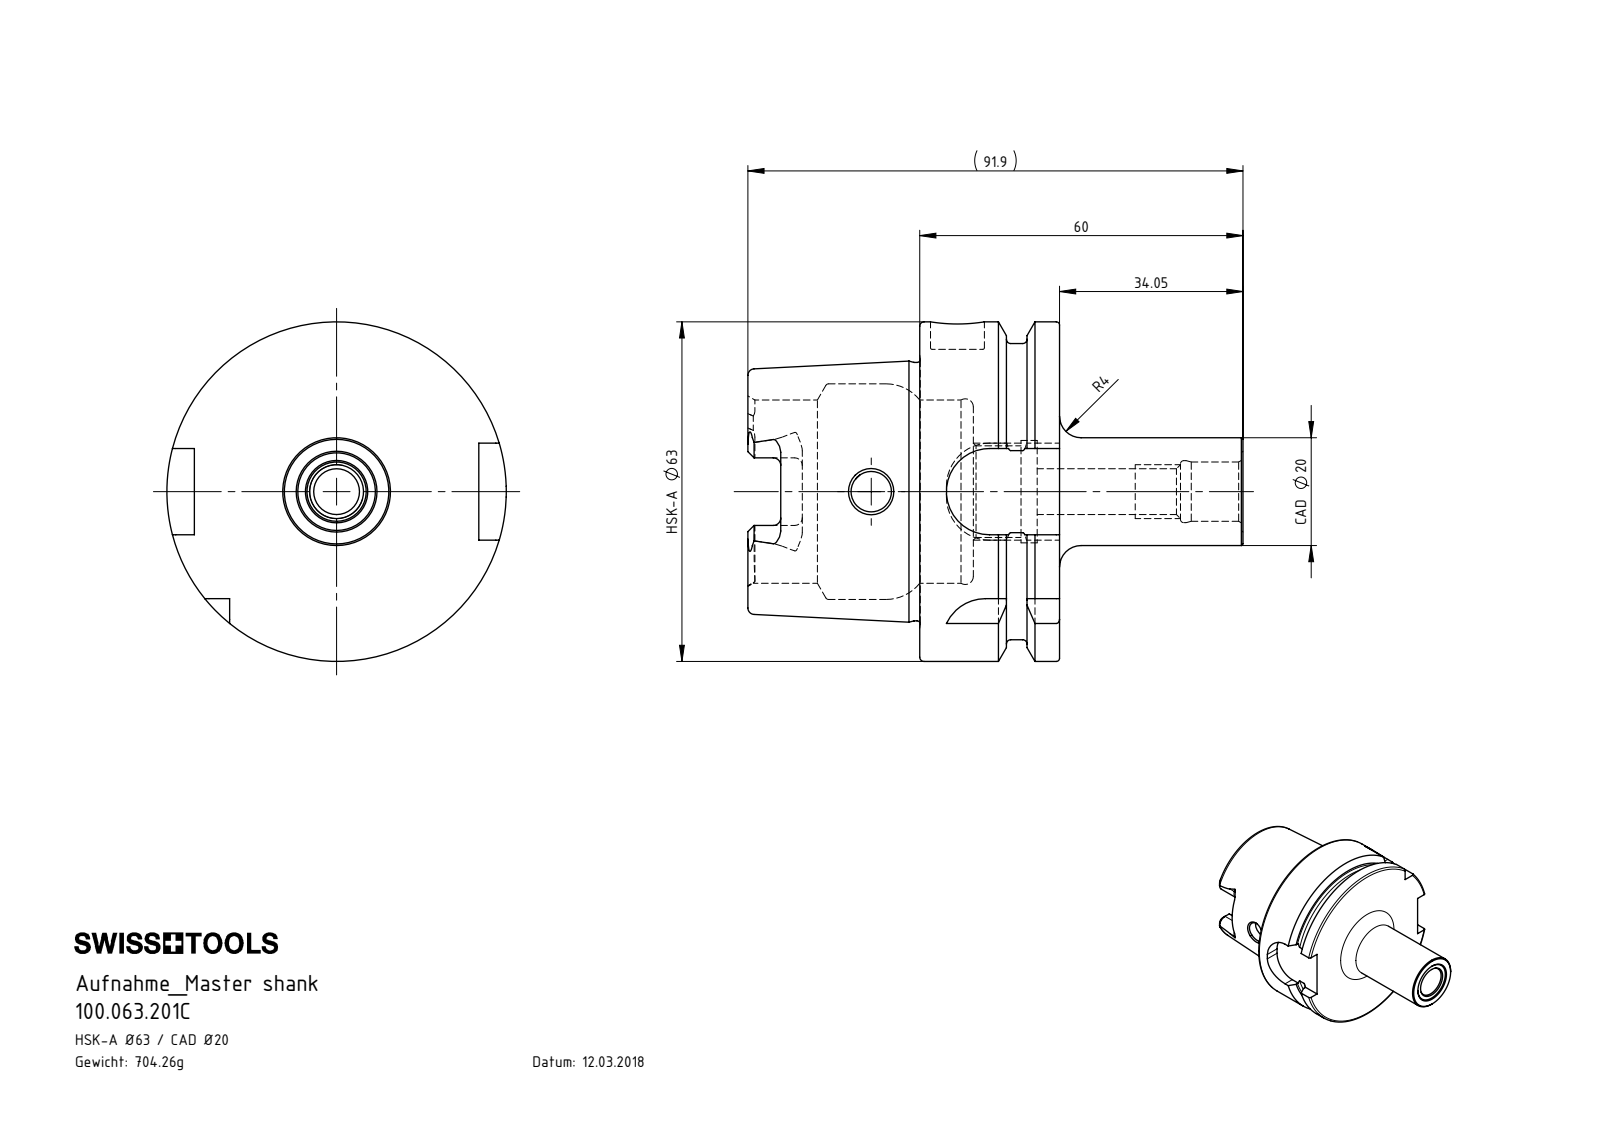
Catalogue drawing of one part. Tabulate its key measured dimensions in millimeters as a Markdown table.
| quantity | value |
| --- | --- |
| part name | HA6.CA1.K01.060 |
| STEP written by | SolidWorks 2017 (AUTOMOTIVE_DESIGN) |
| units | millimeters |
| bodies | 1 solid, 140 faces (48 planar, 33 cylindrical, 59 other) |
| overall size | 91.9 × 63 × 63 |
| volume | 89 747 mm³ |
| surface area | 25 183 mm² |
| round holes (diameter × count) | 7.5 × 1, 8.5 × 1, 10 × 1, 11 × 1, 11.5 × 1, 17 × 1, 19 × 1, 34 × 1, 40 × 1 |
| round bosses / shafts (diameter × count) | 63 × 1, 54.95 × 1, 47.94 × 1, 20 × 1 |
| partial cylindrical surfaces (radius × count) | 1.4 × 6, 2.88 × 4, 8 × 4 |
| main face-to-face distances | 25.95, 16, 9.95, 31.9, 41.85, 57.85, 52.8, 21.8, 11.85, 53.7 |
